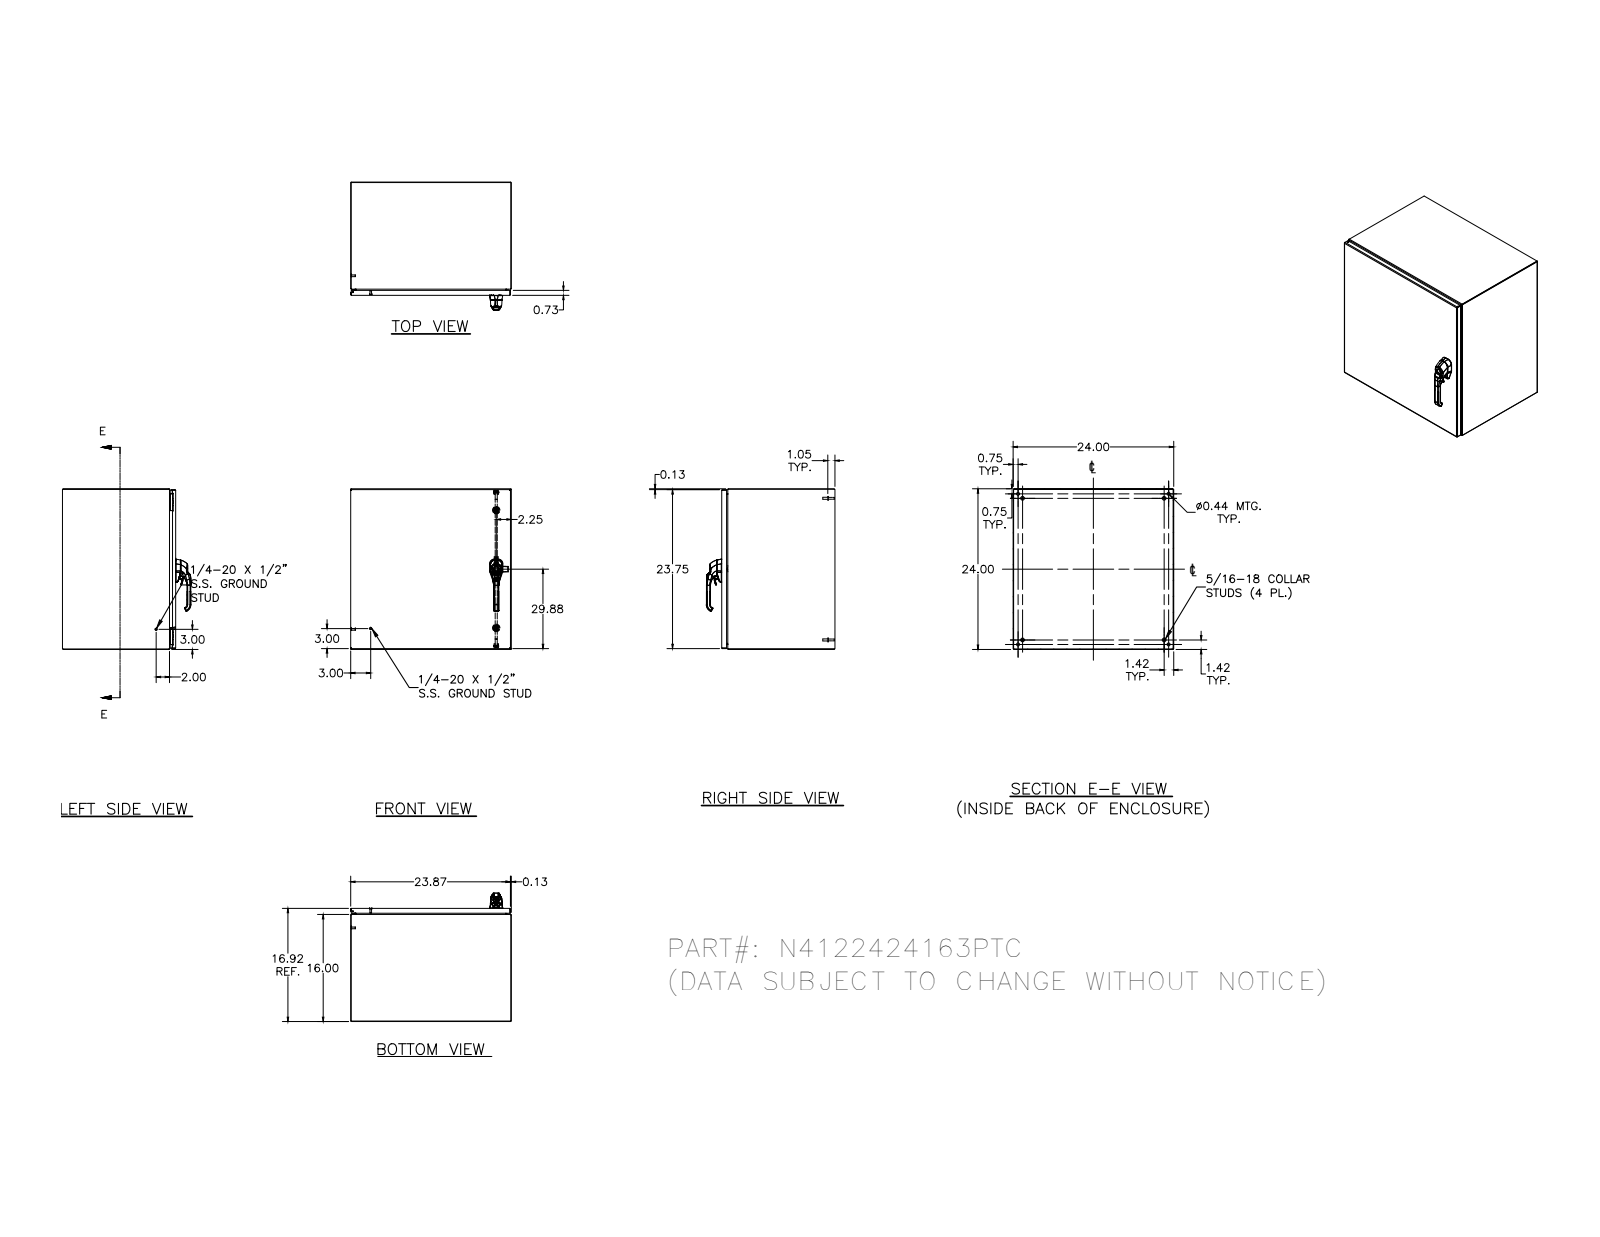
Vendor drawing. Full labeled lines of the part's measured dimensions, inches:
Part name (STEP PRODUCT): N4122424163PTC
STEP written by: SolidWorks 2018 (AUTOMOTIVE_DESIGN)
Units: inches
Bodies: 53 solids, 1618 faces (587 planar, 576 cylindrical, 455 other)
Overall size (bounding box): 24 × 24 × 19.095
Volume: 225.8 in³ · Surface area: 5 866 in²
Round holes (diameter × count): ⌀0.188 ×5, ⌀0.093 ×4, ⌀0.152 ×4, ⌀0.165 ×4, ⌀0.167 ×4, ⌀0.172 ×4, ⌀0.197 ×4, ⌀0.438 ×4, ⌀0.106 ×2, ⌀0.156 ×2, ⌀0.16 ×2, ⌀0.169 ×2
Round bosses / shafts (diameter × count): ⌀0.25 ×10, ⌀0.563 ×4, ⌀0.36 ×4, ⌀0.32 ×4, ⌀0.3 ×4, ⌀0.256 ×4, ⌀0.236 ×4, ⌀0.164 ×4
Partial cylindrical surfaces — rounded edges, fillets, slot ends (radius × count): R0.031 ×28, R0.05 ×26, R0.016 ×18, R0.02 ×18, R0.105 ×18, R0.118 ×16, R0.125 ×14, R0.032 ×8
Main face-to-face distances: 0.074, 23.926, 16.843, 23.852, 24, 16.917, 16.769, 15.926, 0.917, 0.739
Hole centre spacings: 20, 0.017, 0.66, 22.5, 21.368, 22.869, 0.019, 0.5
